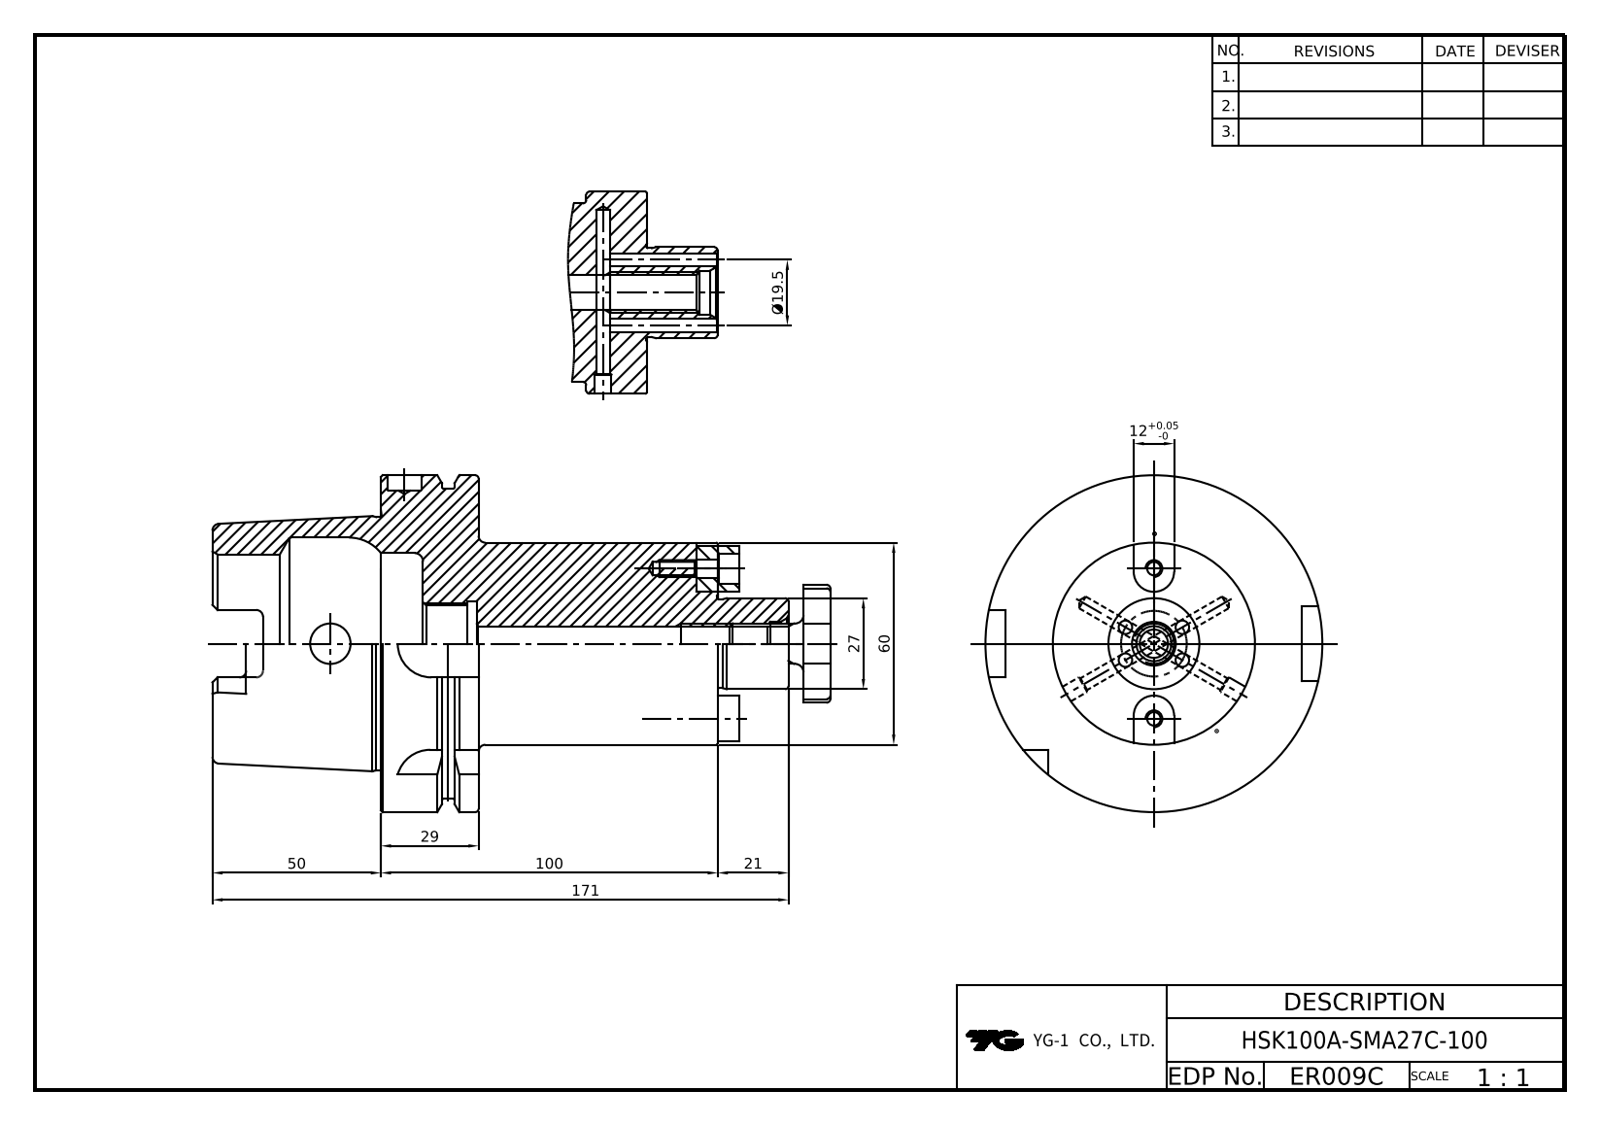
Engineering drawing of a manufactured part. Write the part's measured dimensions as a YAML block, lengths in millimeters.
part_name: "LO-HSK100A-SMA27C-100; SMA27E-DRIVE KEY-SECO; HEX'' WRENCH BOLT-M5x0.8x15L; SMA27-COLLAR BOLT"
step_written_by: "Autodesk Inventor 2025 (AP242_MANAGED_MODEL_BASED_3D_ENGINEERING_MIM_LF)"
units: millimeters
bodies: {solids: 6, faces: 217, planar: 85, cylindrical: 69, other: 63}
overall_size: [189, 100, 100]
volume: 467031
surface_area: 76203
round_holes:
  - {diameter: 4, count: 4}
  - {diameter: 4.13, count: 2}
  - {diameter: 5.5, count: 2}
  - {diameter: 9, count: 2}
  - {diameter: 10, count: 1}
  - {diameter: 10.11, count: 1}
  - {diameter: 12, count: 1}
  - {diameter: 13, count: 1}
  - {diameter: 22.38, count: 1}
  - {diameter: 25, count: 1}
  - {diameter: 53, count: 1}
  - {diameter: 63, count: 1}
round_bosses_or_shafts:
  - {diameter: 8.5, count: 2}
  - {diameter: 5, count: 2}
  - {diameter: 100, count: 1}
  - {diameter: 92, count: 1}
  - {diameter: 75.41, count: 1}
  - {diameter: 60, count: 1}
  - {diameter: 27, count: 1}
  - {diameter: 12, count: 1}
partial_cylinders:
  - {radius: 1.2, count: 8}
  - {radius: 2, count: 6}
  - {radius: 3, count: 4}
  - {radius: 4.88, count: 4}
  - {radius: 6, count: 4}
  - {radius: 10, count: 4}
  - {radius: 17.5, count: 1}
face_to_face_distances: [29, 100, 71, 12.5, 16.5, 87.5, 50, 62.5, 79, 150]
hole_center_spacings: [9.75, 19.36, 28.46, 9.76, 16.88, 19.5, 22.3, 44.6]
